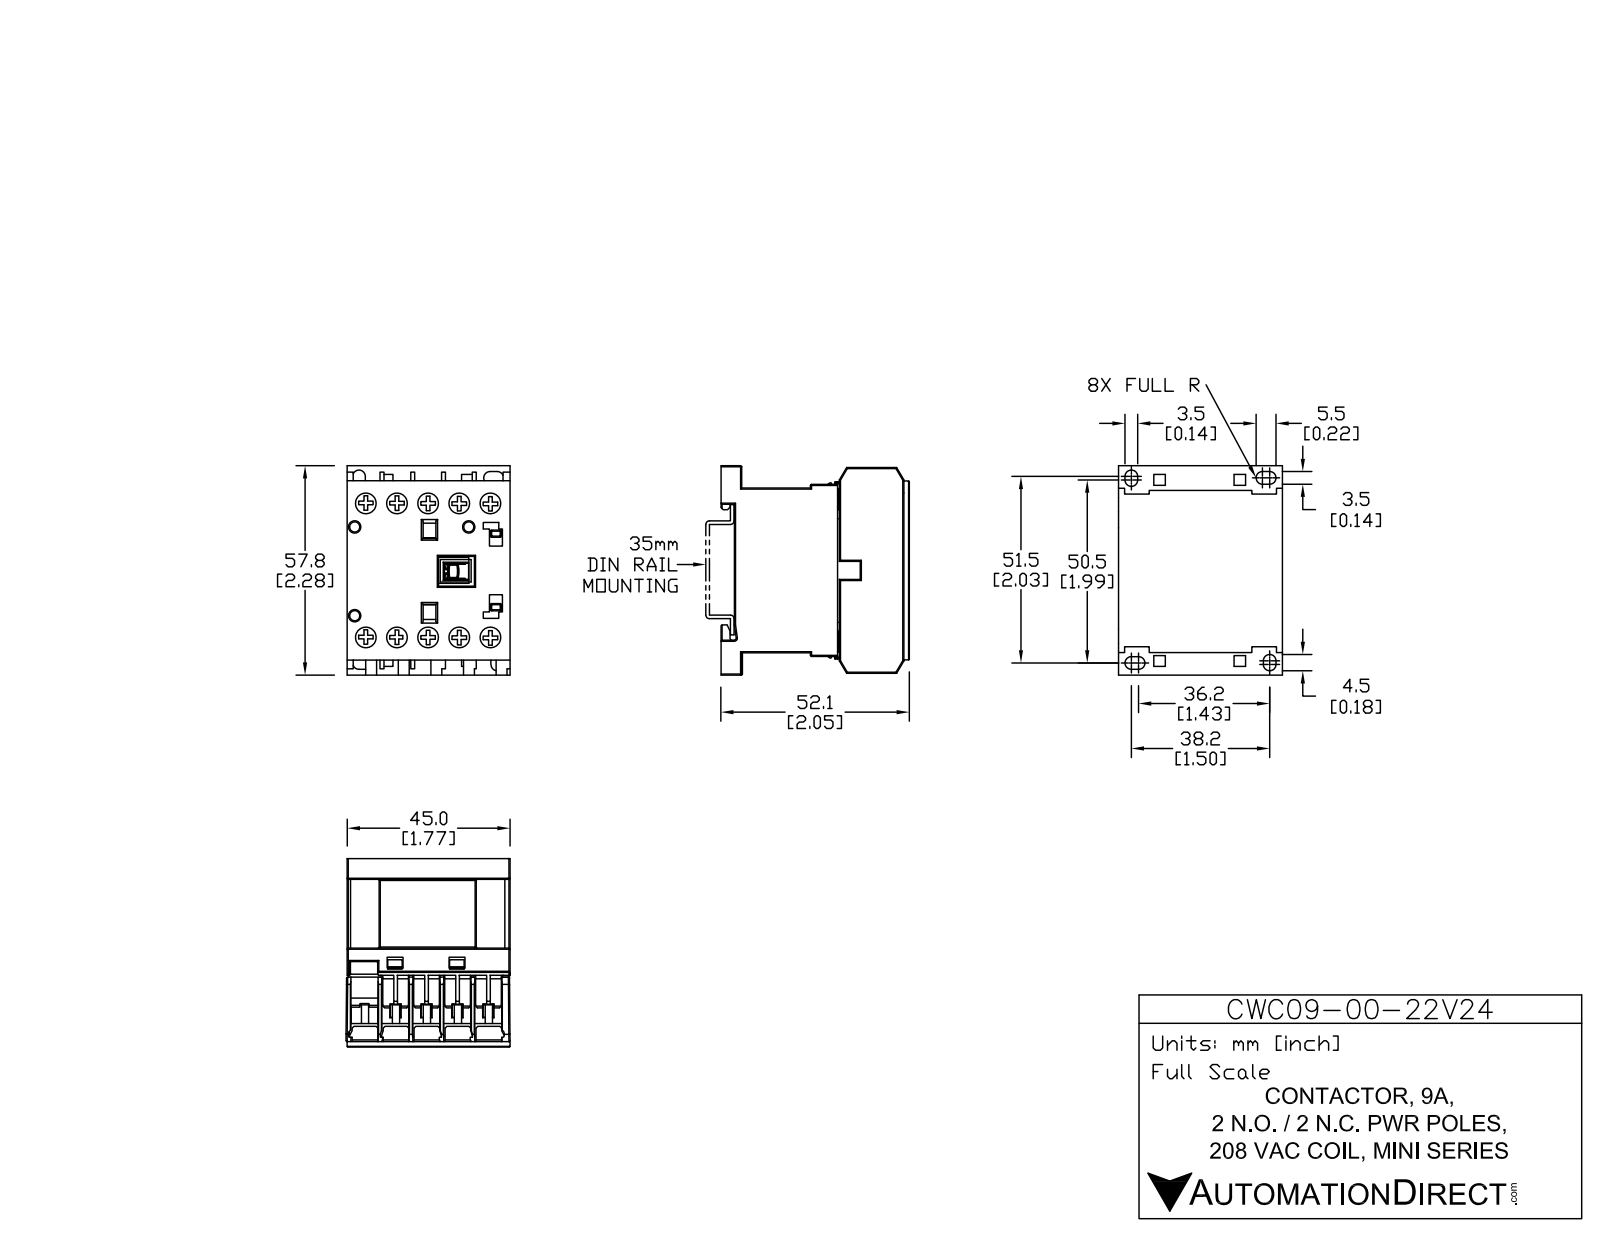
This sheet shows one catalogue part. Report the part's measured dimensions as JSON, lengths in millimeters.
{"part_name": "CWC09-00-22V24", "step_written_by": "SolidWorks 2013 (AUTOMOTIVE_DESIGN)", "units": "millimeters", "bodies": {"solids": 15, "faces": 535, "planar": 445, "cylindrical": 90, "other": 0}, "overall_size": [58.04, 52.12, 45.75], "volume_mm3": 97133, "surface_area_mm2": 30437, "round_holes": [[6.2, 10], [2.8, 3]], "round_bosses_or_shafts": [[5.9, 10]], "partial_cylinders_radius": [[0.3, 20], [1.72, 6], [1.73, 2], [0.32, 1], [0.42, 1], [0.55, 1]], "face_to_face_distances": [8.25, 45.5, 1.25, 16.5, 9.5, 5.5, 17.75, 5.13, 10.63, 7], "hole_center_spacings": [8.55, 37.94, 17.1, 40.72, 36.96, 25.65, 44.99, 6.91]}
